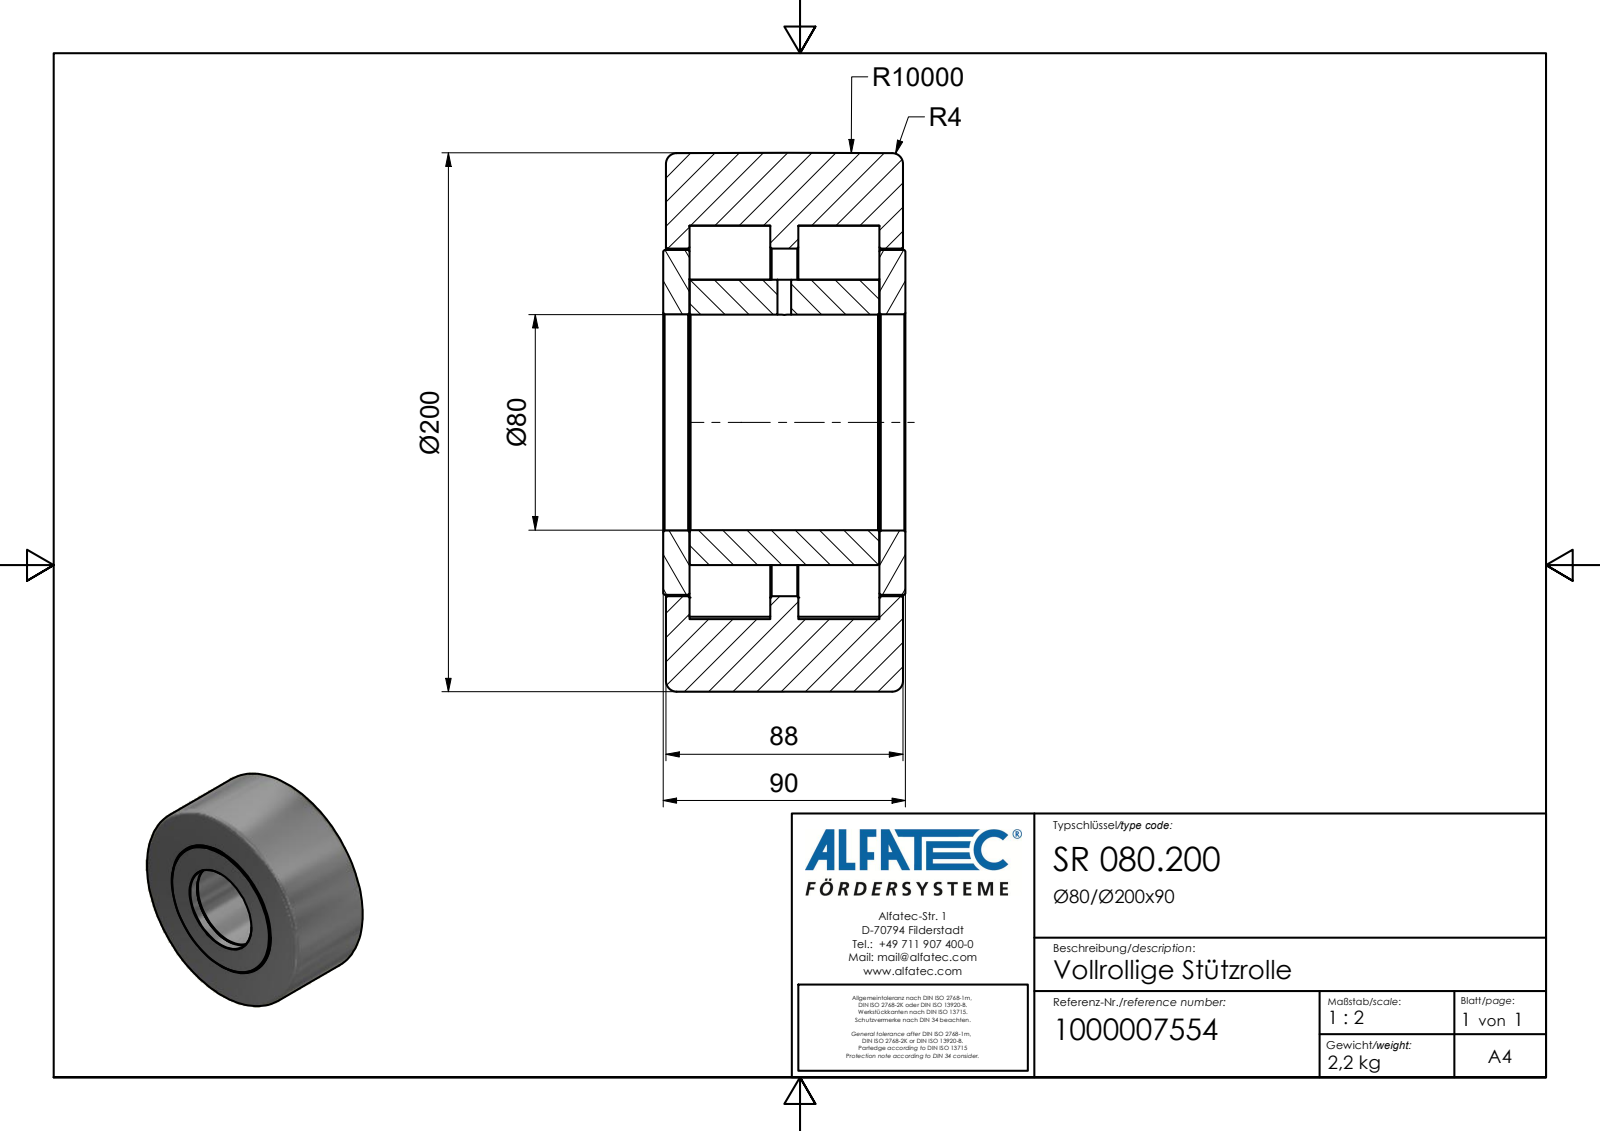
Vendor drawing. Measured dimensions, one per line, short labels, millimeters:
name: SR 080.200_Kontur
written by: Autodesk Inventor 2020 (AUTOMOTIVE_DESIGN)
unit: mm
bodies: 2 solids, 45 faces (12 planar, 12 cylindrical, 21 other)
size: 200 × 200 × 90
volume: 1 808 000 mm³; area: 220 492 mm²
holes: 1× ⌀5, 1× ⌀80, 1× ⌀80.2, 1× ⌀129, 1× ⌀146
bosses: 1× ⌀128, 1× ⌀106
face distances: 88, 8.75, 79.25, 1, 9.75, 80.25, 89, 70.5, 90, 39.75
